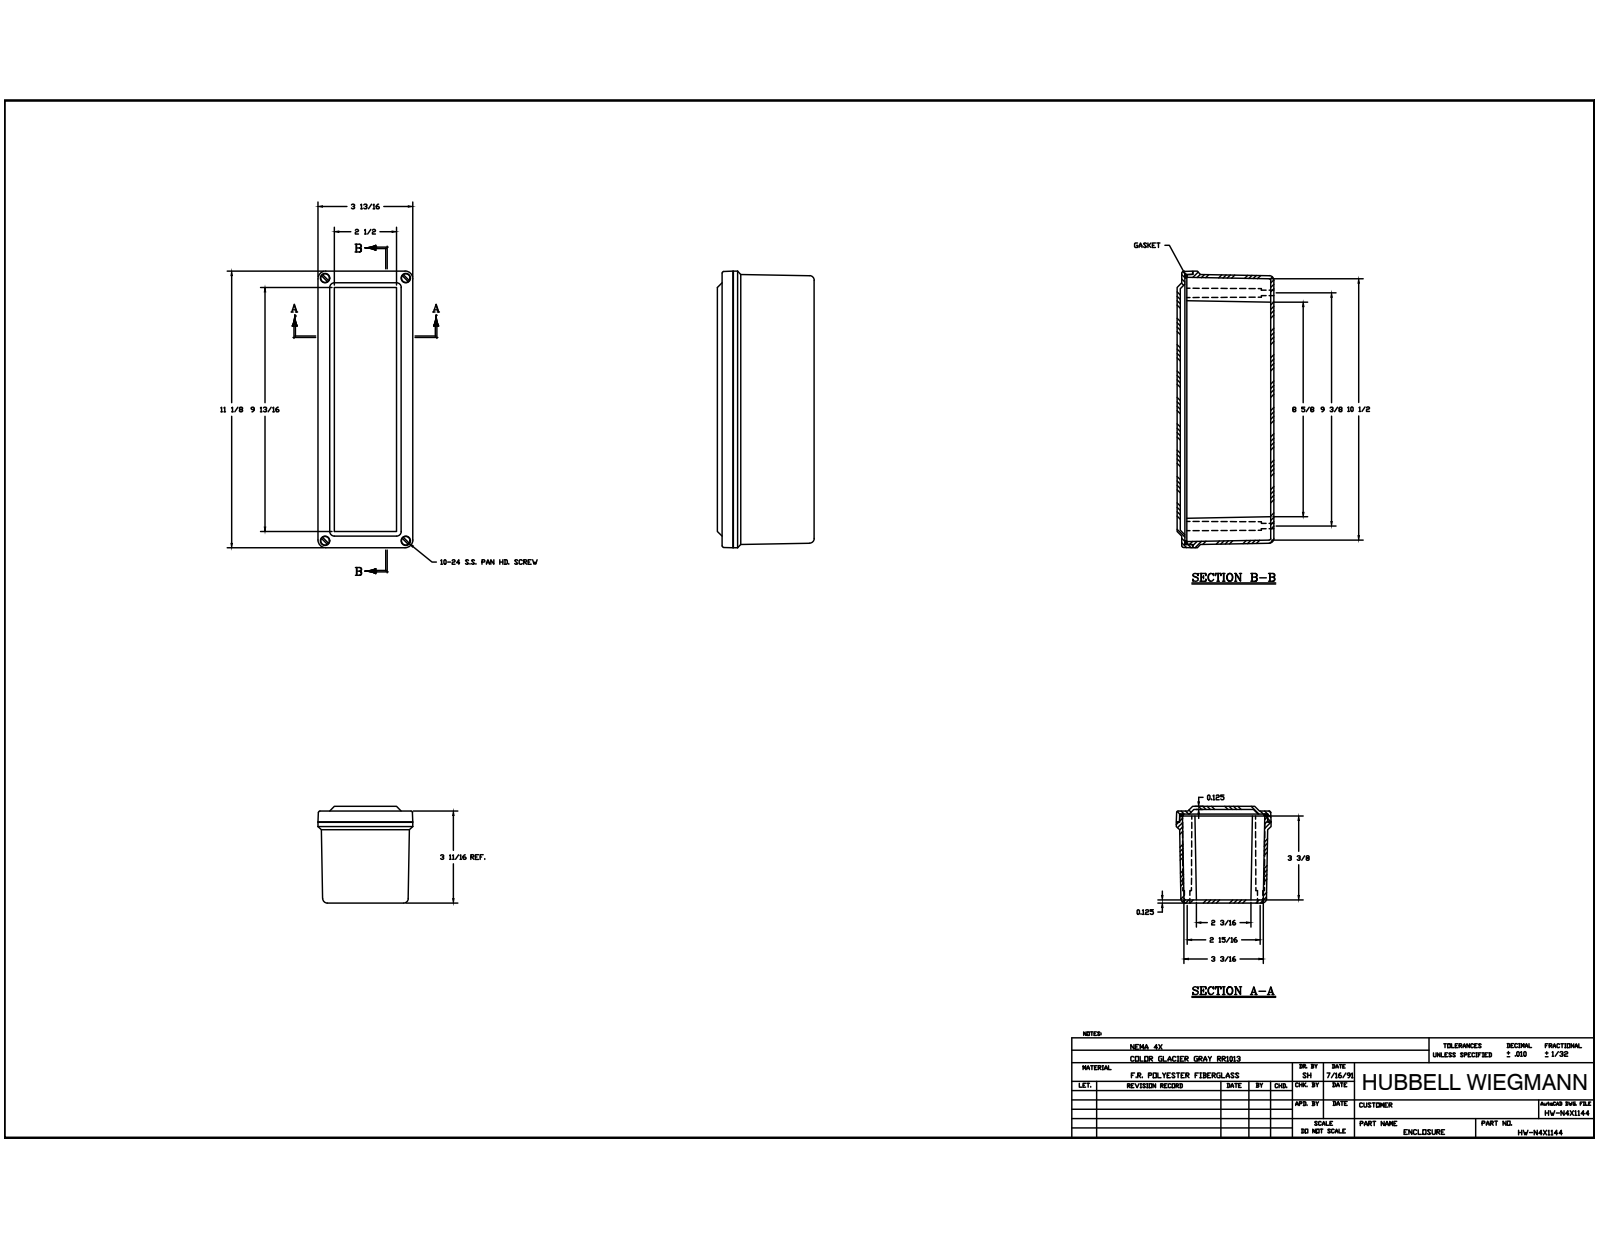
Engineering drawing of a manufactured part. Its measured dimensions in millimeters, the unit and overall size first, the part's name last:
Units: millimetres
Overall size (bounding box): 282.57 × 98.42 × 96.84
Round holes (diameter × count): ⌀5.56 ×8, ⌀3.68 ×4, ⌀4.83 ×4, ⌀9.52 ×4
Round bosses / shafts (diameter × count): ⌀9.42 ×4, ⌀5.54 ×4, ⌀4.5 ×4
Partial cylindrical surfaces — rounded edges, fillets, slot ends (radius × count): R0.79 ×20, R0.3 ×16, R1.59 ×4, R4.47 ×4, R4.76 ×4, R5.59 ×4, R7.94 ×4, R8.26 ×4
Main face-to-face distances: 3.17, 3.34, 95.25, 4.76, 98.42, 92.08, 90.49, 12.7, 1.59, 87.32
Hole centre spacings: 15.59, 80.01, 253.23, 265.11, 74.62, 82.54, 238.12, 249.54
Volume: 476 385 mm³ · Surface area: 262 194 mm²
Bodies: 11 solids, 379 faces (183 planar, 100 cylindrical, 96 other)
Part name (STEP PRODUCT): WPCF1144 BOX; 10-24 X 0.4375 DP BRASS INSERT; WPCF1144 CVR; WPCF1144 GASKET (+3 more)
STEP written by: Autodesk Inventor 2014 (AUTOMOTIVE_DESIGN)
